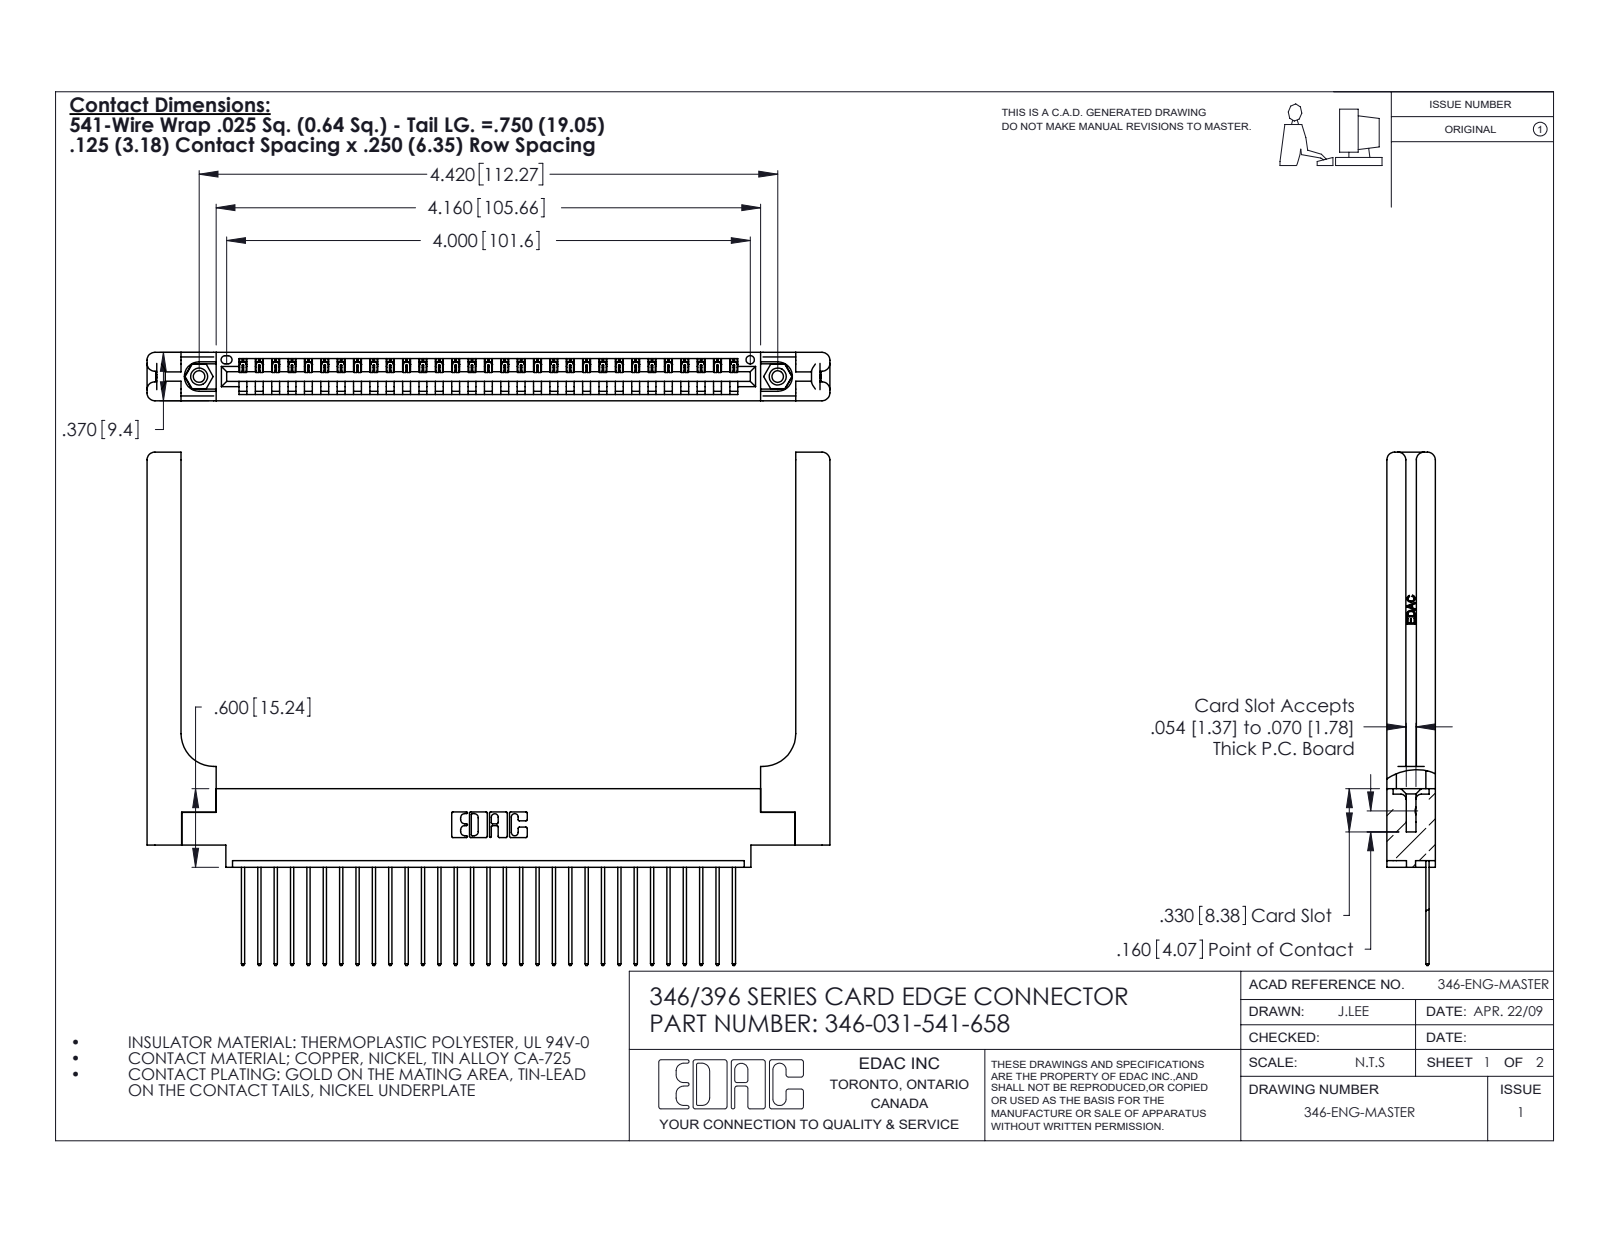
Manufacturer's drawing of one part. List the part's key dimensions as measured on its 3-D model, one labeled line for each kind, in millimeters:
Part name (STEP PRODUCT): 345-250-001_345-250-001-102; 346 Part_0.170 Offset - 0.156 Dia-TH; 345-292-001_345-293-141; 346-220-058_345-220-058 (+1 more)
STEP written by: SolidWorks 2020 (CONFIG_CONTROL_DESIGN)
Units: millimetres
Bodies: 36 solids, 2194 faces (1482 planar, 652 cylindrical, 60 other)
Overall size (bounding box): 132.5 × 99.6 × 9.4
Volume: 20 060 mm³ · Surface area: 21 520 mm²
Round holes (diameter × count): ⌀2.3 ×2, ⌀3.2 ×2, ⌀4 ×2, ⌀1.6 ×1
Round bosses / shafts (diameter × count): ⌀3.9 ×2
Partial cylindrical surfaces — rounded edges, fillets, slot ends (radius × count): R0.2 ×62, R0.3 ×62, R0.3 ×22, R1.5 ×16, R0.2 ×6, R0.8 ×6, R0.7 ×3, R0.8 ×2
Main face-to-face distances: 9.4, 1.8, 1.2, 8.2, 3.8, 3.8, 7.6, 0.6, 6.4, 5.6
Hole centre spacings: 6.2, 107, 112.3
